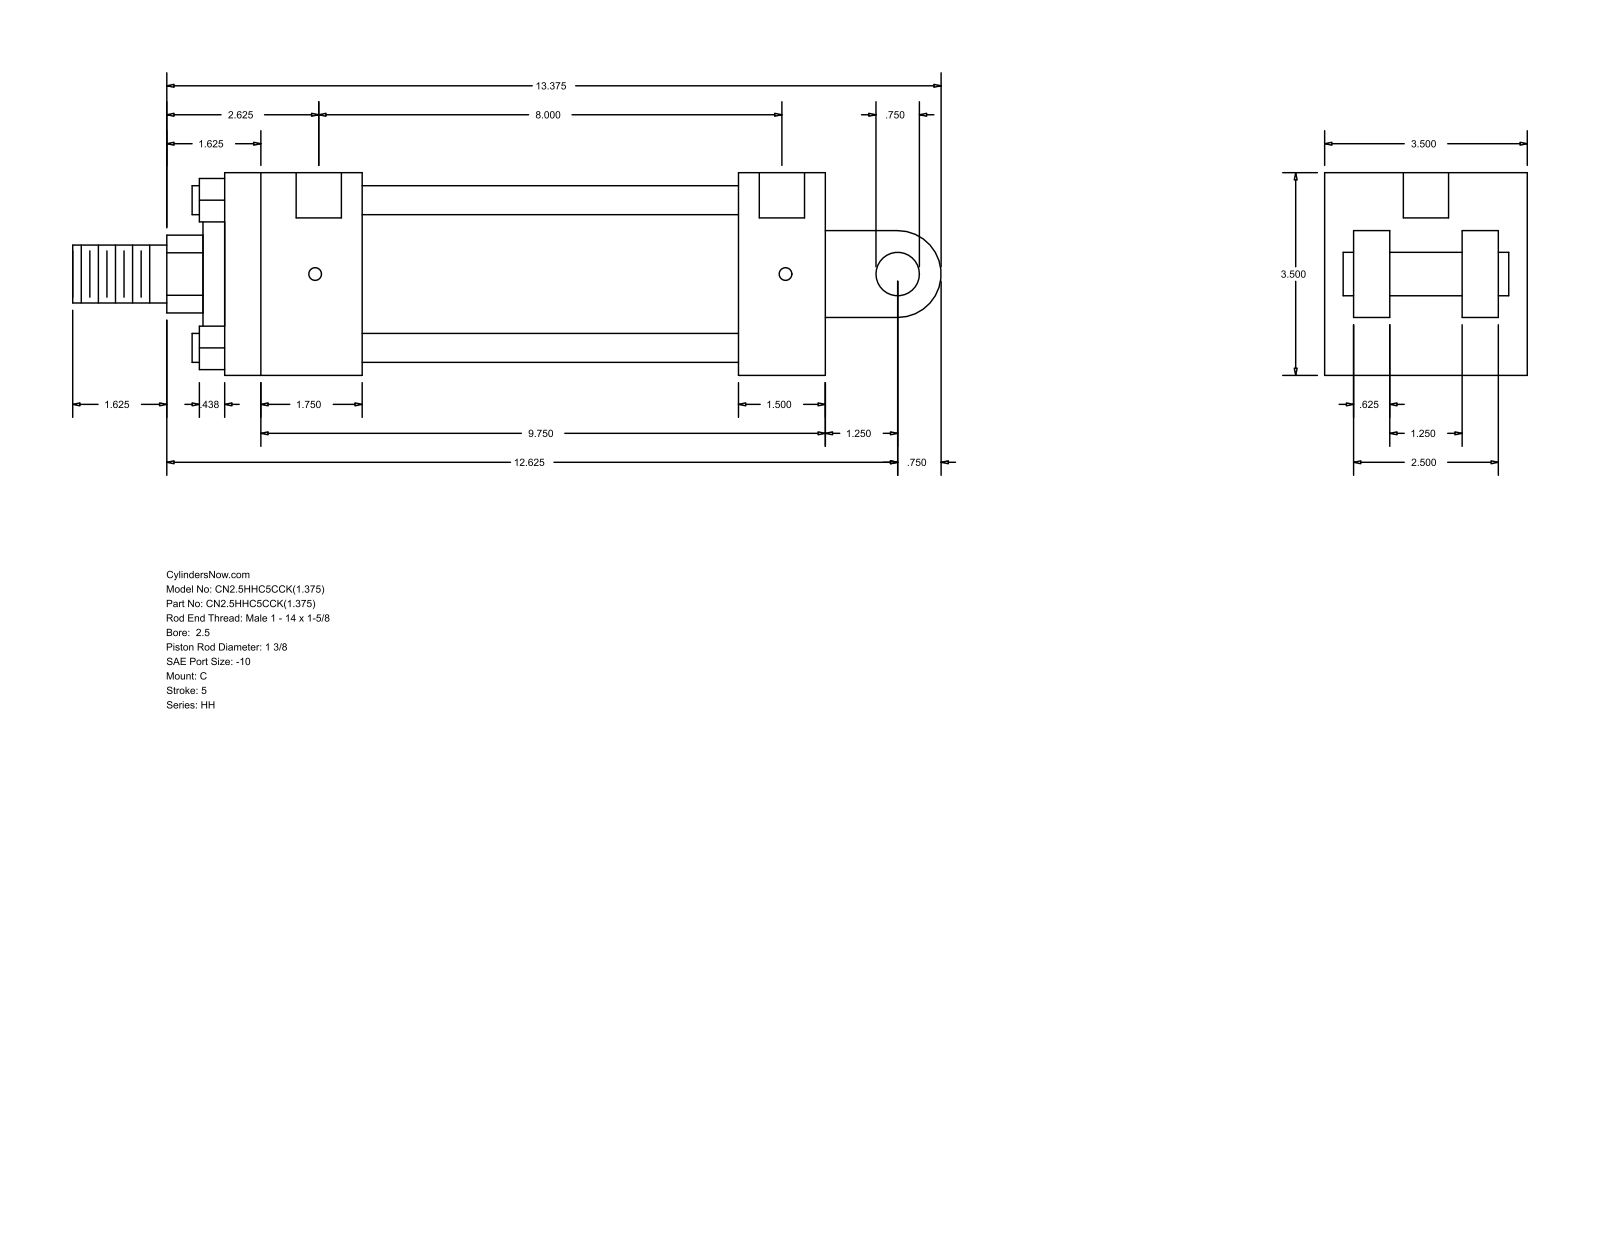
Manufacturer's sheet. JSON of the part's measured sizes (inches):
{"part_name": "HH_C__0250_1.375", "step_written_by": "GSSL Pune (CONFIG_CONTROL_DESIGN)", "units": "inches", "bodies": {"solids": 0, "faces": 99, "planar": 70, "cylindrical": 29, "other": 0}, "overall_size": [15, 3.5, 3.5], "round_holes": [[0.219, 4], [0.781, 2]], "round_bosses_or_shafts": [[0.5, 4], [2.875, 1], [2, 1], [1.375, 1], [1, 1], [0.75, 1]], "partial_cylinders_radius": [[0.672, 1], [0.75, 1]], "face_to_face_distances": [3.5, 10.375, 2.5, 0.5, 8.875, 1.5, 2.375, 6.5, 8, 3], "hole_center_spacings": [0.062, 8.063, 8.125, 8]}
